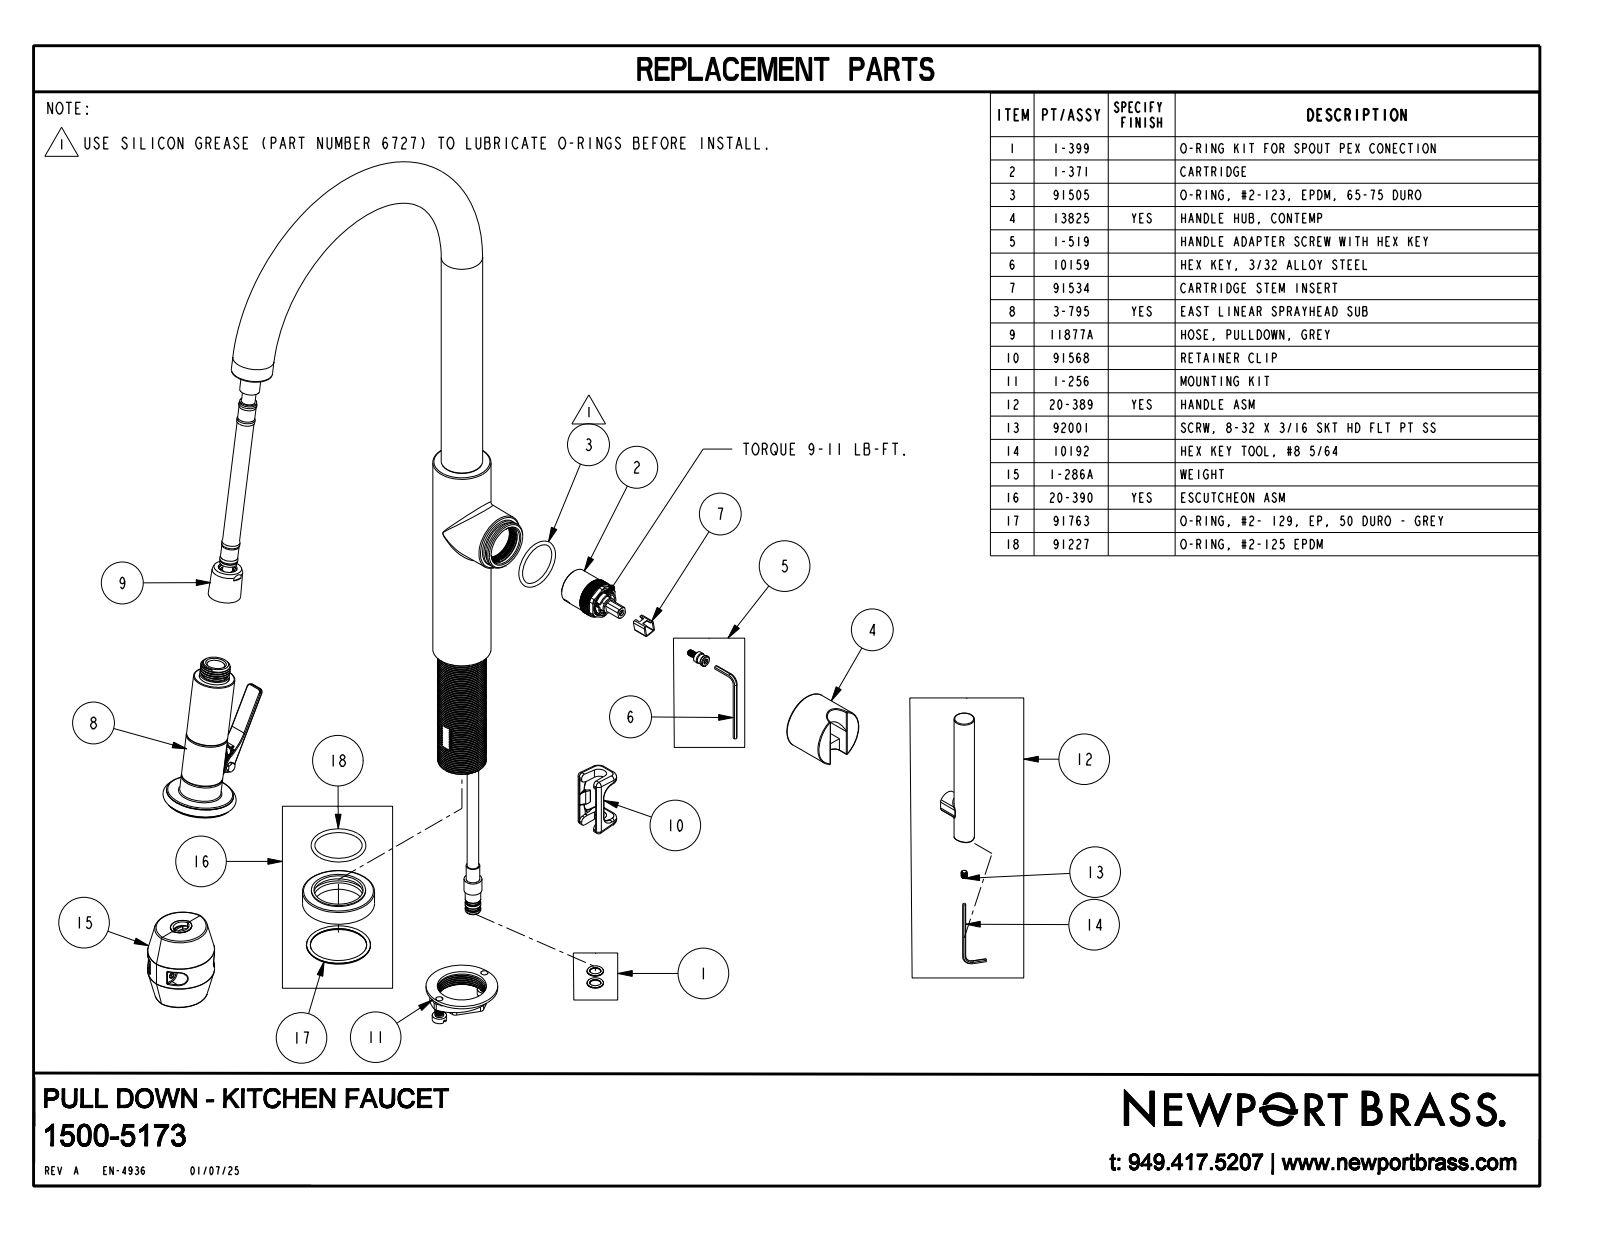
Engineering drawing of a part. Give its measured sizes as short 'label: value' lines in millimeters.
name: 1500-5143
written by: CREO PARAMETRIC BY PTC INC, 2023134 (CONFIG_CONTROL_DESIGN)
unit: mm
bodies: 1 solid, 1320 faces (829 planar, 262 cylindrical, 229 other)
size: 463.7 × 272.5 × 102.3
volume: 708 600 mm³; area: 101 500 mm²
holes: 18× ⌀1, 1× ⌀4.3, 1× ⌀5.3, 1× ⌀12, 1× ⌀14.2, 1× ⌀26.3, 1× ⌀35.4
bosses: 18× ⌀2.6, 2× ⌀29, 1× ⌀50.3, 1× ⌀47.1, 1× ⌀40.6, 1× ⌀40.1, 1× ⌀38.3, 1× ⌀29
rounds: 32× R0.5, 27× R0.8, 17× R1.5, 5× R0.6, 4× R0.3, 4× R0.8, 4× R1.1, 4× R3
face distances: 7.8, 1.1, 10.8, 19.5, 18.4, 171.1, 160.3, 2.5, 1, 6.8
hole spacings: 9.3, 3.3, 9.4, 6.4, 16.2, 18.4, 17.6, 9.3
